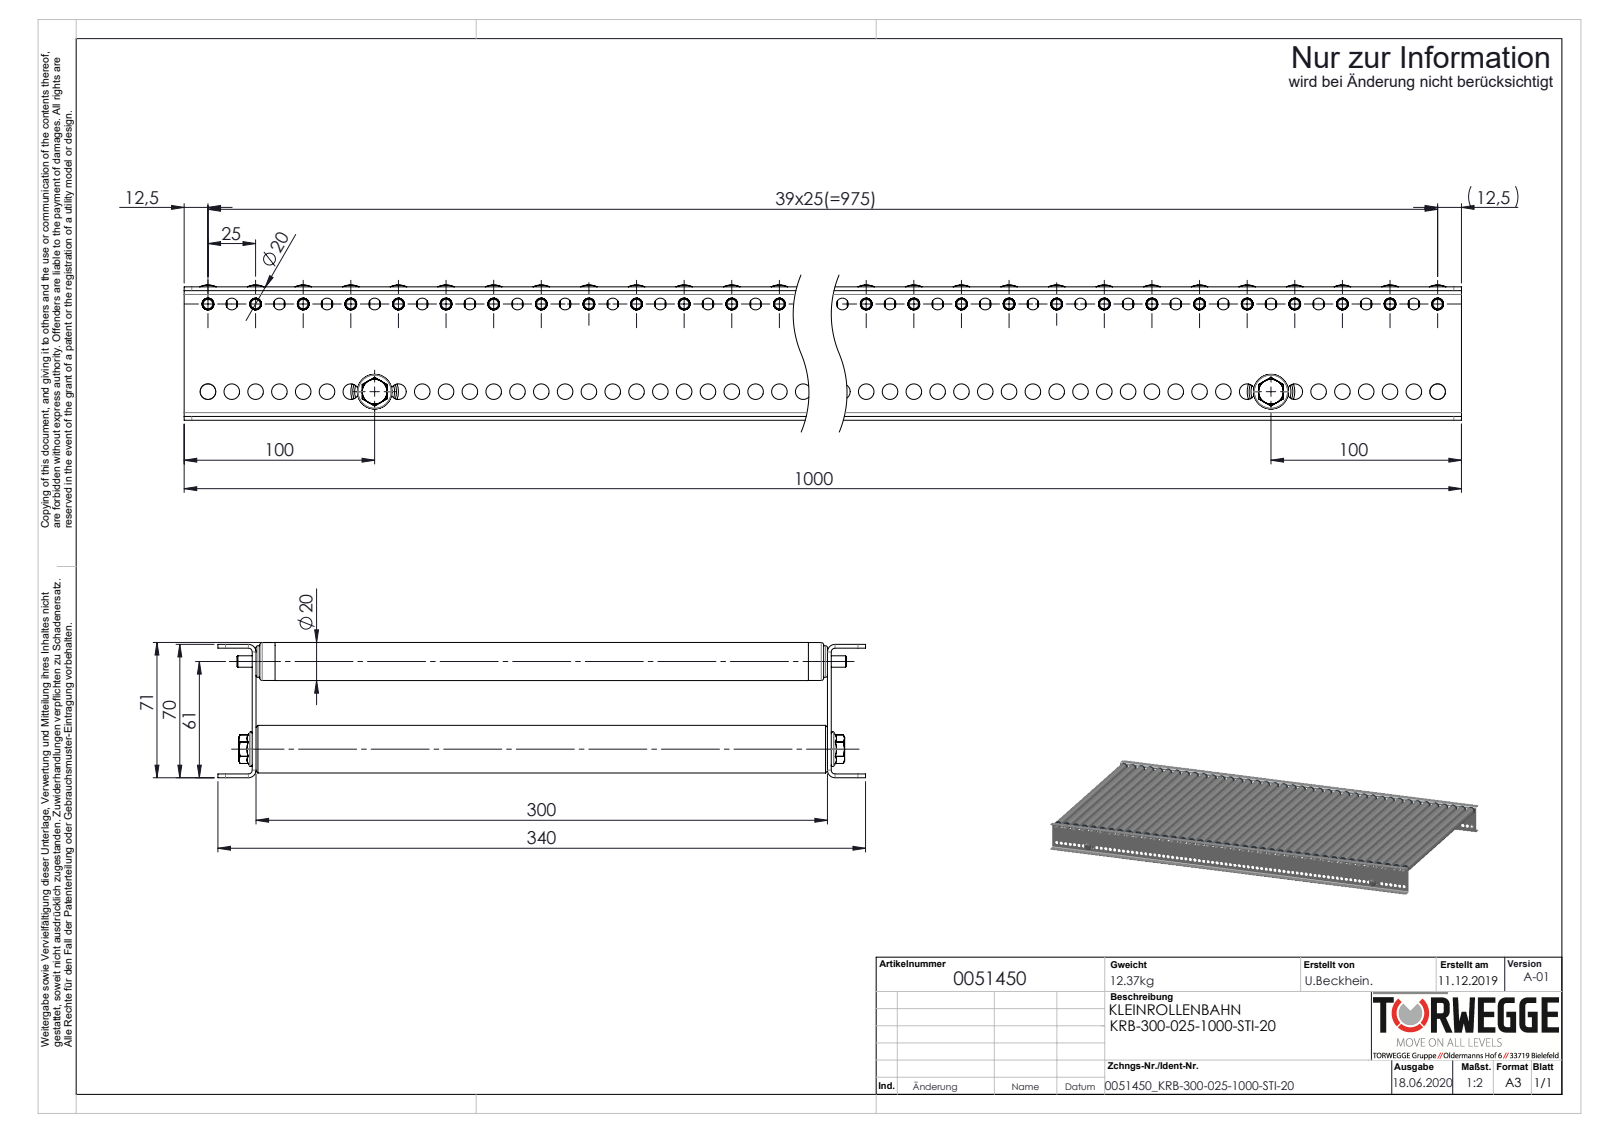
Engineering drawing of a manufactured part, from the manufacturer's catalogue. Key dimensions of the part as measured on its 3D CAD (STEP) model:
Part name (STEP PRODUCT): S100992_Typ-KUT50-20x1-6; 0051450; KUT50-20x1,5-STI-A6_FA-EL=KFG_S100909_KUT50-20x1-STI-A6-FA-EL=300; 0039777_Achse-Ø06-FA-KFG_L=320 fr D20 (+4 more)
STEP written by: SolidWorks 2020 (AUTOMOTIVE_DESIGN)
Units: millimetres
Bodies: 92 solids, 7952 faces (2600 planar, 3008 cylindrical, 2344 other)
Overall size (bounding box): 1000 × 340 × 71
Volume: 1 532 000 mm³ · Surface area: 2 350 000 mm²
Round holes (diameter × count): ⌀6.2 ×79, ⌀8.2 ×79, ⌀6.1 ×40, ⌀14.2 ×40, ⌀17.2 ×40, ⌀18 ×40, ⌀6.8 ×2, ⌀21 ×2
Round bosses / shafts (diameter × count): ⌀20 ×40, ⌀19.9 ×40, ⌀18.1 ×40, ⌀17.8 ×40, ⌀16.5 ×40, ⌀6 ×40, ⌀25 ×2, ⌀8 ×2
Partial cylindrical surfaces — rounded edges, fillets, slot ends (radius × count): R4.05 ×40, R4 ×8, R2 ×4
Main face-to-face distances: 2, 302, 68, 300, 304, 66, 70, 292, 18, 30
Hole centre spacings: 12.5, 25, 37.5, 50, 62.5, 75, 87.5, 100
